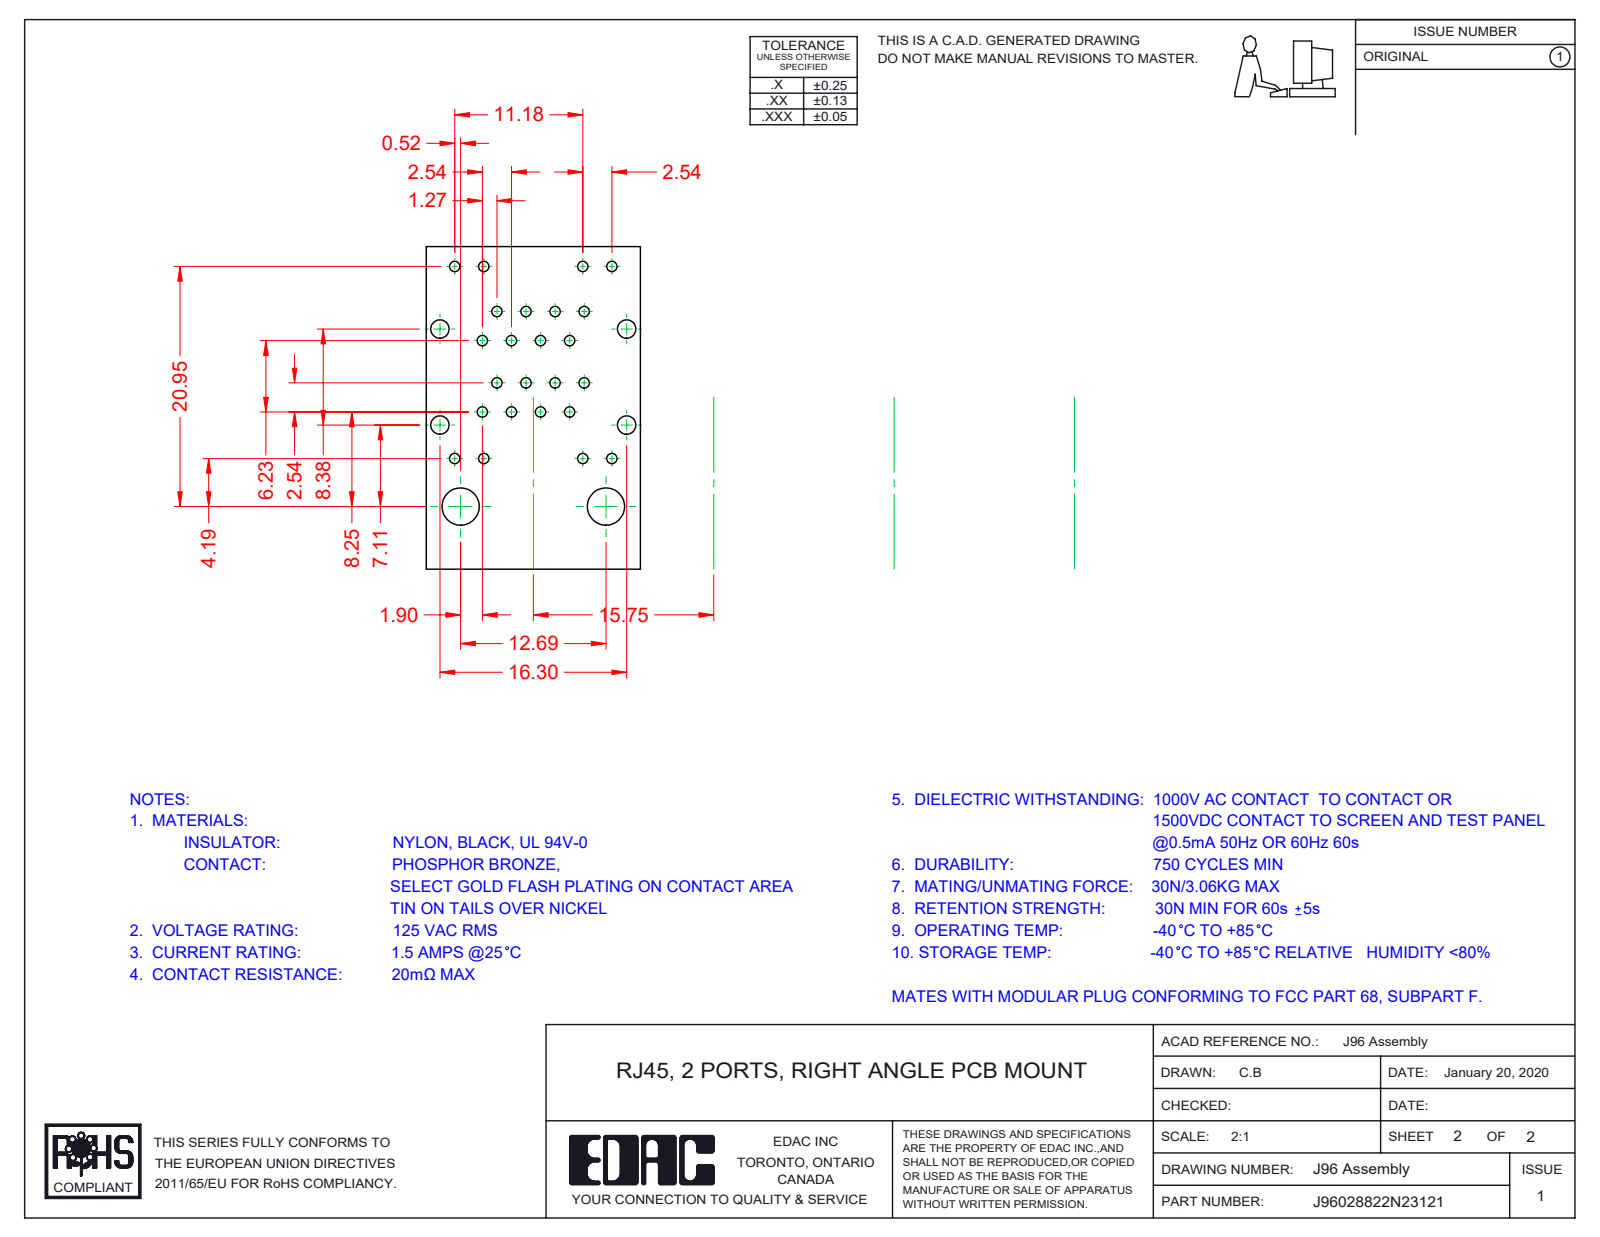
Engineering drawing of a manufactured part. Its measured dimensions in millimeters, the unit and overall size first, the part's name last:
Units: millimetres
Overall size (bounding box): 29.58 × 28.68 × 16.8
Partial cylindrical surfaces — rounded edges, fillets, slot ends (radius × count): R0.25 ×48, R0.15 ×32, R0.35 ×24, R0.5 ×16, R1 ×16, R0.2 ×13, R0.7 ×9, R2 ×5
Main face-to-face distances: 16.3, 16.1, 1.75, 16.5, 14.75, 1.55, 14.55, 0.53, 1.48, 11.2
Volume: 6 852 mm³ · Surface area: 19 109 mm²
Bodies: 27 solids, 2382 faces (1849 planar, 427 cylindrical, 106 other)
Part name (STEP PRODUCT): 96 Contacts Lower; 96 Insulator Insert; 96 Shield_2 Ports LED - No EMI; 96 Contact Lock Lower (+8 more)
STEP written by: SolidWorks 2016 (CONFIG_CONTROL_DESIGN)
